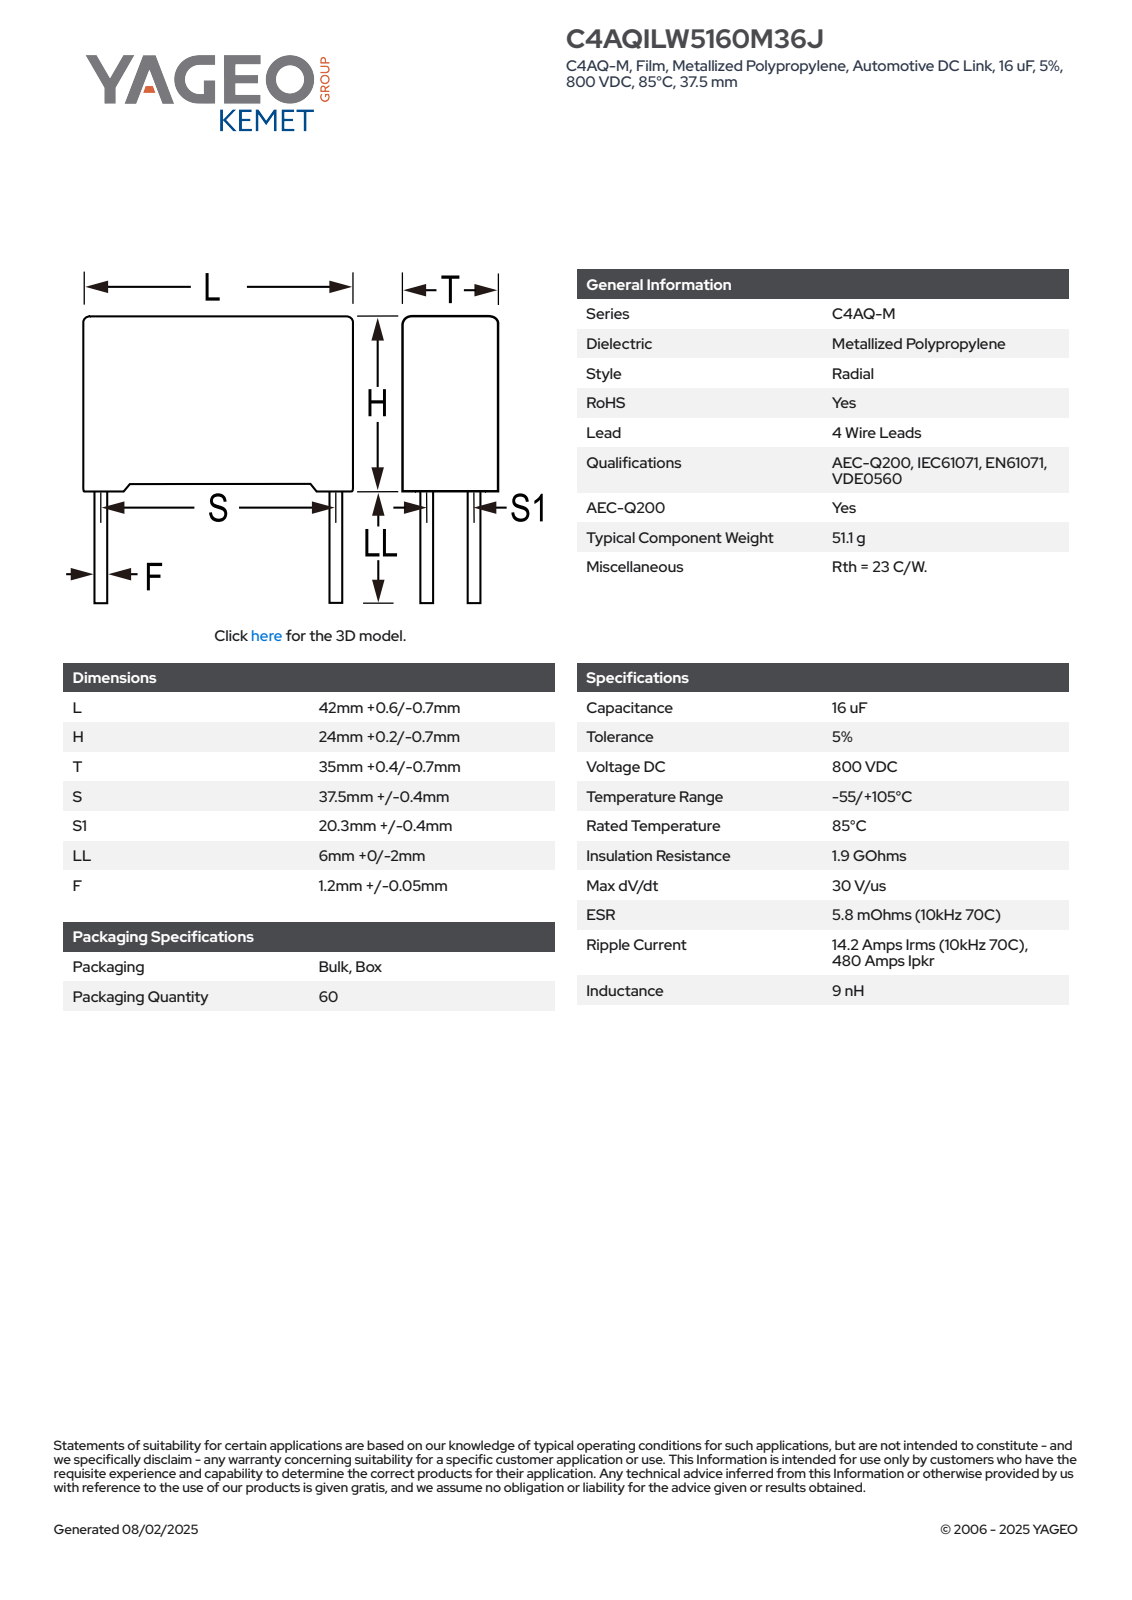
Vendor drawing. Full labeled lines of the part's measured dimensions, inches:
Part name (STEP PRODUCT): CFP_RB4_42X24X35_L42.6H24.2T35.4S37.5S120.3LL6F1.25
STEP written by: SolidWorks 2014 (AUTOMOTIVE_DESIGN)
Units: inches
Bodies: 4 solids, 91 faces (83 planar, 8 cylindrical, 0 other)
Overall size (bounding box): 1.677 × 1.394 × 1.189
Volume: 2.172 in³ · Surface area: 10.9 in²
Round bosses / shafts (diameter × count): ⌀0.049 ×4
Main face-to-face distances: 0.925, 1.394, 1.677, 0.028, 0.953, 1.394, 0.086, 1.591, 1.506, 1.308
